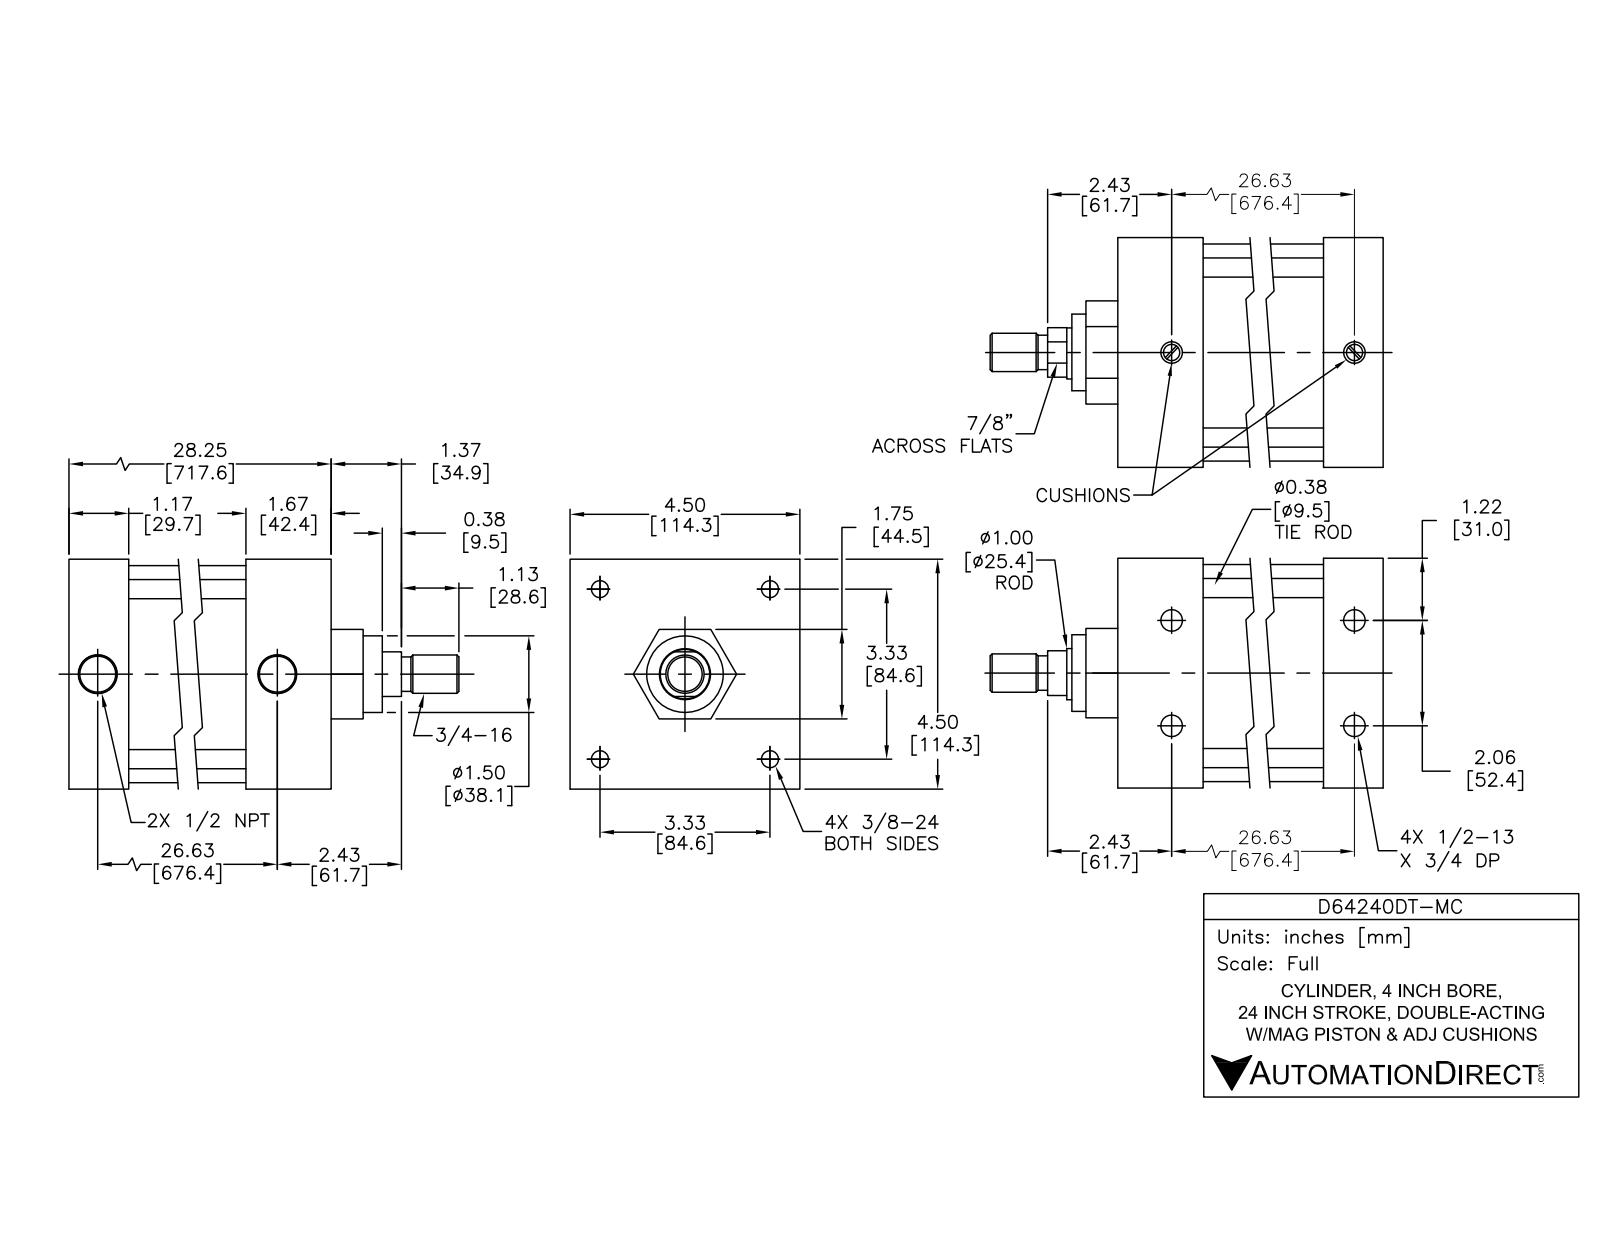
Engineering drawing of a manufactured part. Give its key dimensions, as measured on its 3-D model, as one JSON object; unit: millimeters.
{"part_name": "D64240DT-M PISTON; D64240DT-M BODY; D64240DT-MC", "step_written_by": "SolidWorks 2015 (AUTOMOTIVE_DESIGN)", "units": "millimeters", "bodies": {"solids": 12, "faces": 303, "planar": 99, "cylindrical": 114, "other": 90}, "overall_size": [780.9, 114.3, 114.3], "volume_mm3": 2355000, "surface_area_mm2": 703200, "round_holes": [[8.4, 4], [10.3, 4], [10.6, 4], [15.9, 4], [12.7, 2], [19.5, 2], [25.4, 1], [25.5, 1], [101.6, 1]], "round_bosses_or_shafts": [[15.5, 4], [9.5, 4], [8.6, 4], [108, 1], [101.5, 1], [44.5, 1], [25.3, 1], [24.6, 1]], "partial_cylinders_radius": [[11.4, 4]], "face_to_face_distances": [114.3, 2, 643.3, 717.4, 44.5, 685.7, 31.7, 654.1, 31.6, 63.4], "hole_center_spacings": [59.7, 84.4, 676.7, 676.2, 26.2, 26.2, 52.4, 119.3]}
